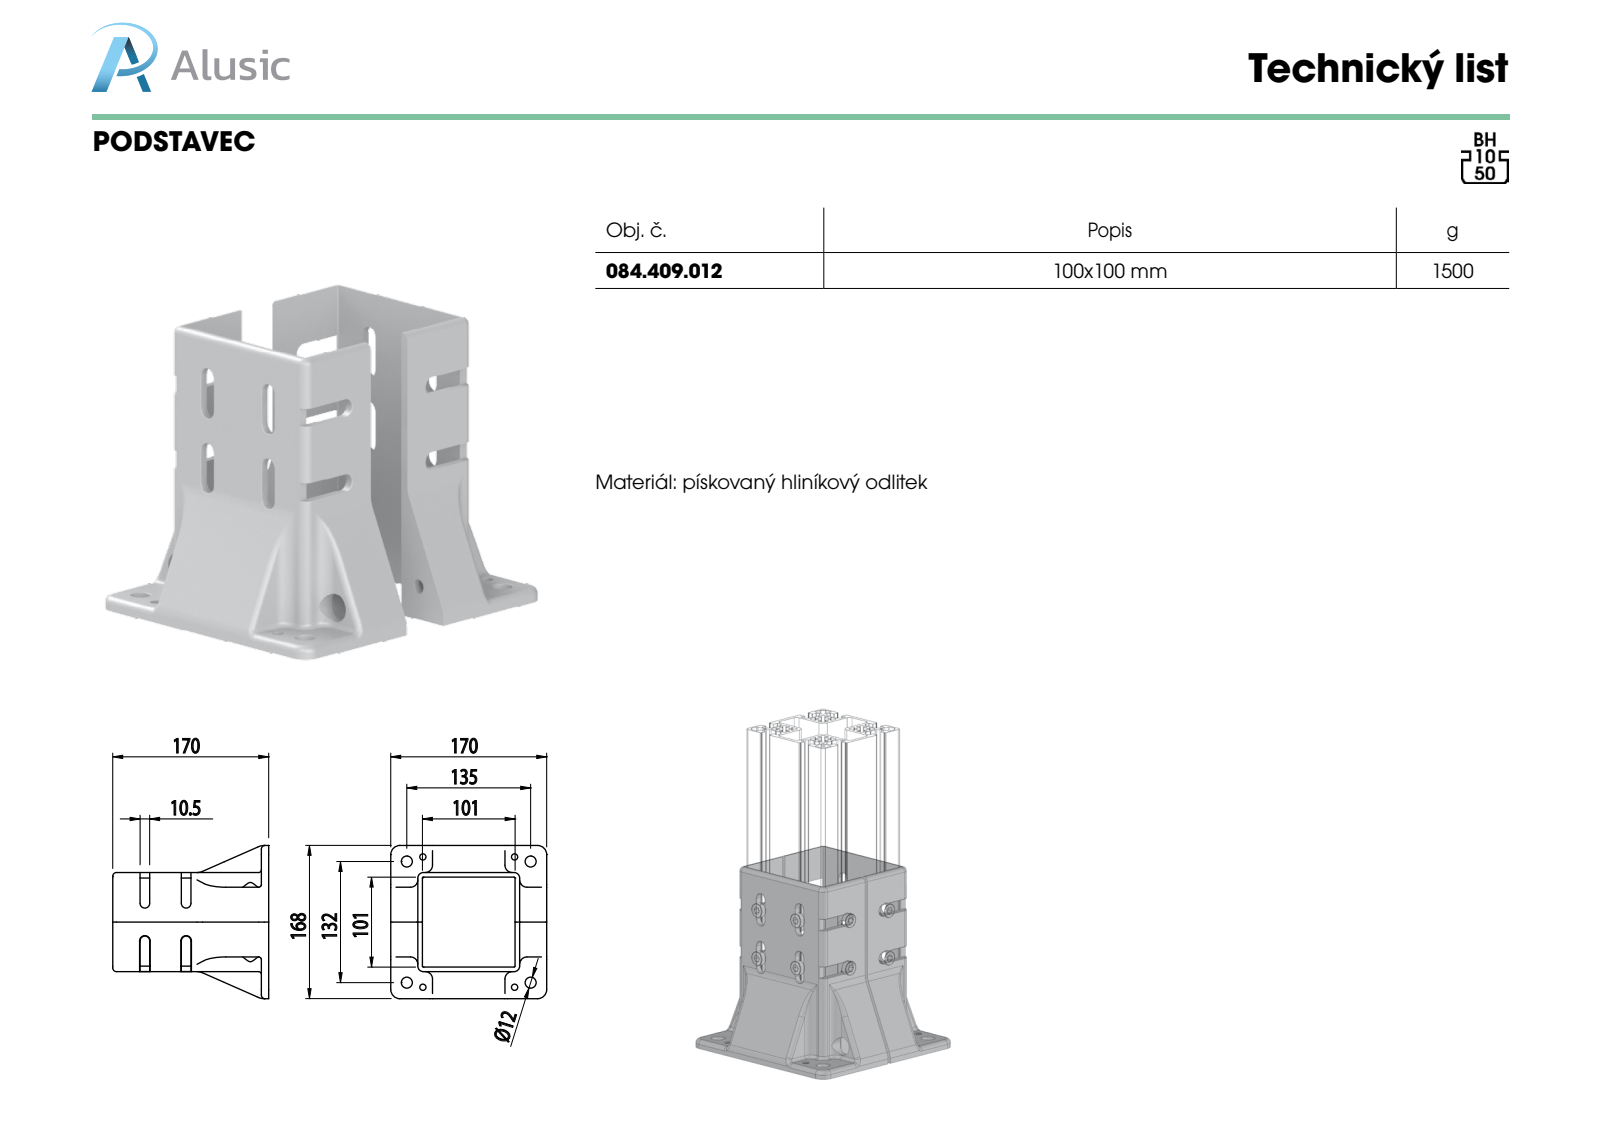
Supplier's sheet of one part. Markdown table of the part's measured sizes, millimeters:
| quantity | value |
| --- | --- |
| part name | 084.409.012 |
| STEP written by | SolidWorks 2012 (CONFIG_CONTROL_DESIGN) |
| units | millimeters |
| bodies | 2 solids, 482 faces (118 planar, 216 cylindrical, 148 other) |
| overall size | 170 × 170 × 169 |
| volume | 544 605 mm³ |
| surface area | 211 135 mm² |
| round holes (diameter × count) | 6.8 × 4, 12 × 4, 8.5 × 2, 17 × 2 |
| partial cylindrical surfaces (radius × count) | 2 × 42, 0.5 × 16, 4 × 16, 5.25 × 12, 3 × 8, 8 × 8, 15 × 8, 1 × 4 |
| main face-to-face distances | 5, 105, 106, 100, 101, 110, 56, 49, 111, 54 |
| hole center spacings | 18.2, 117.61, 140.1, 182.01, 100, 134, 135, 144 |
